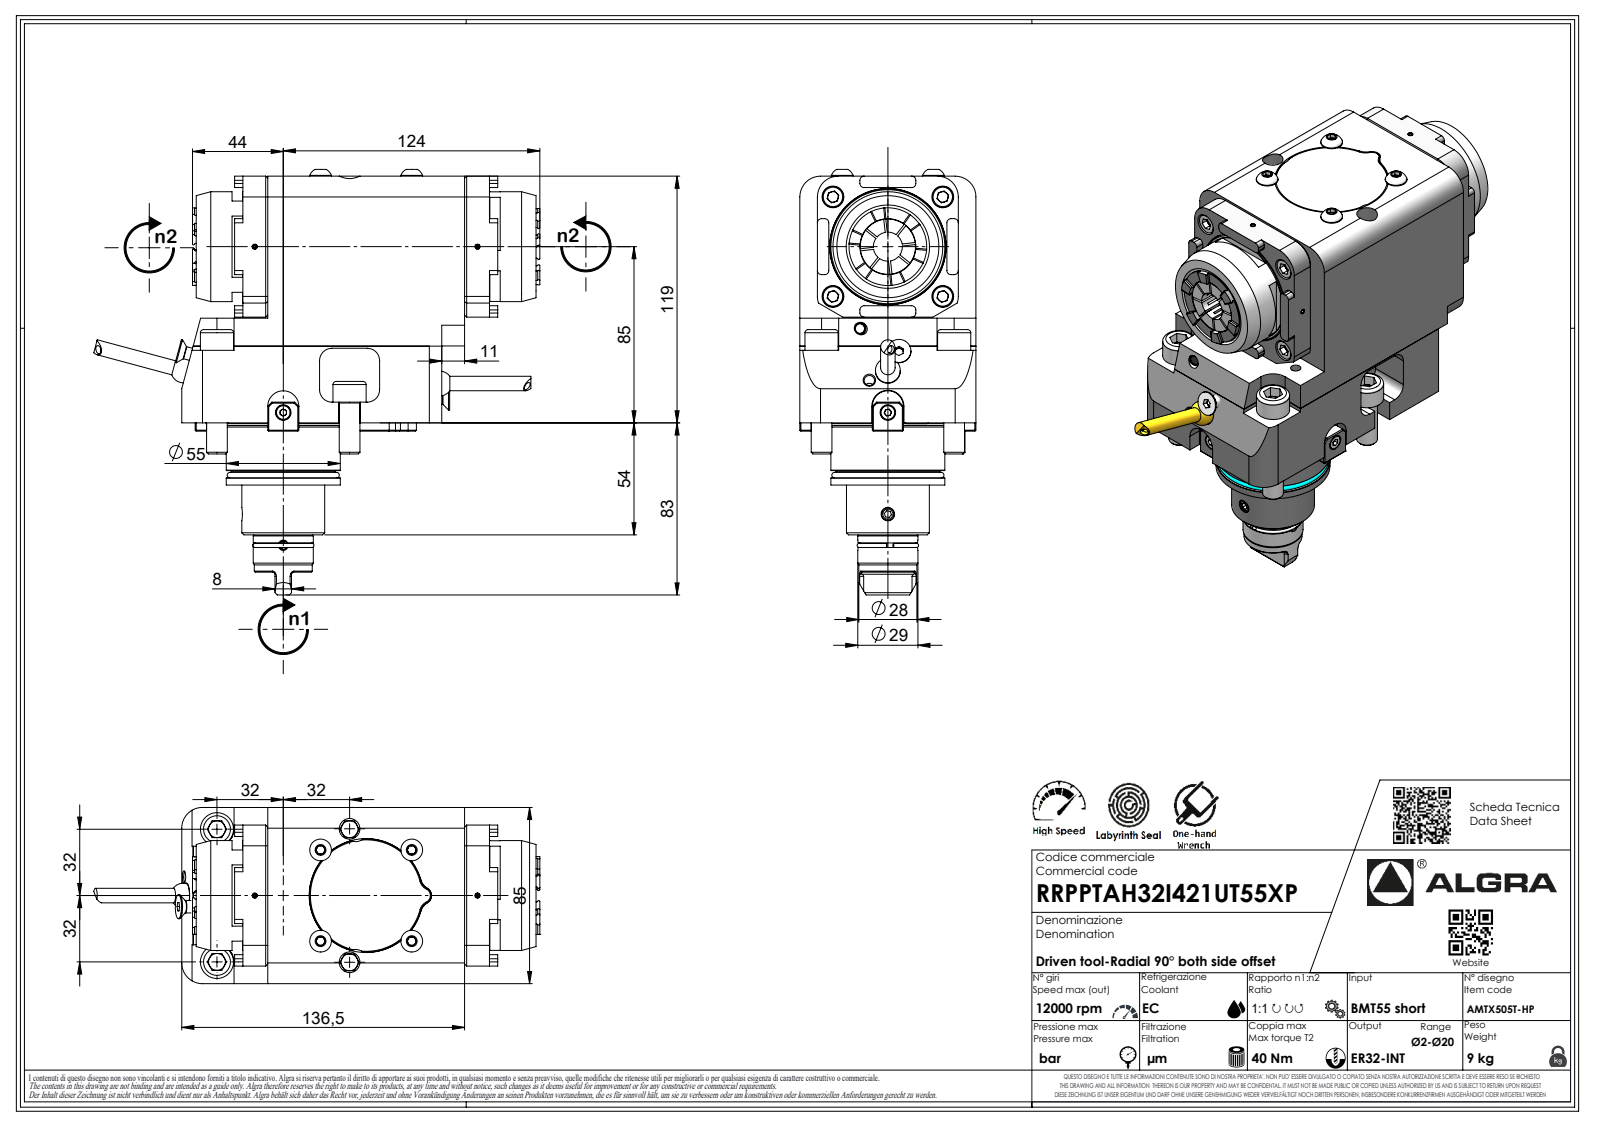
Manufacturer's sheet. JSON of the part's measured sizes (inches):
{"part_name": "RRPPTAH32I421UT55XP", "step_written_by": "SolidWorks 2023 (AUTOMOTIVE_DESIGN)", "units": "inches", "bodies": {"solids": 1, "faces": 699, "planar": 461, "cylindrical": 113, "other": 125}, "overall_size": [8.404, 8.083, 3.346], "volume_in3": 86.04, "surface_area_in2": 155, "round_holes": [[0.157, 2], [0.083, 1], [0.256, 1]], "round_bosses_or_shafts": [[0.413, 4], [0.394, 4], [0.63, 2], [0.276, 2], [2.165, 1], [2.15, 1], [2.087, 1], [1.976, 1]], "partial_cylinders_radius": [[0.079, 24], [0.394, 10], [0.013, 7], [0.02, 7], [0.146, 7], [0.157, 4], [0.039, 2], [0.325, 2]], "face_to_face_distances": [3.346, 4.685, 0.886, 4.213, 0.472, 5.571, 1.358, 5.098, 2.677, 0.433]}
